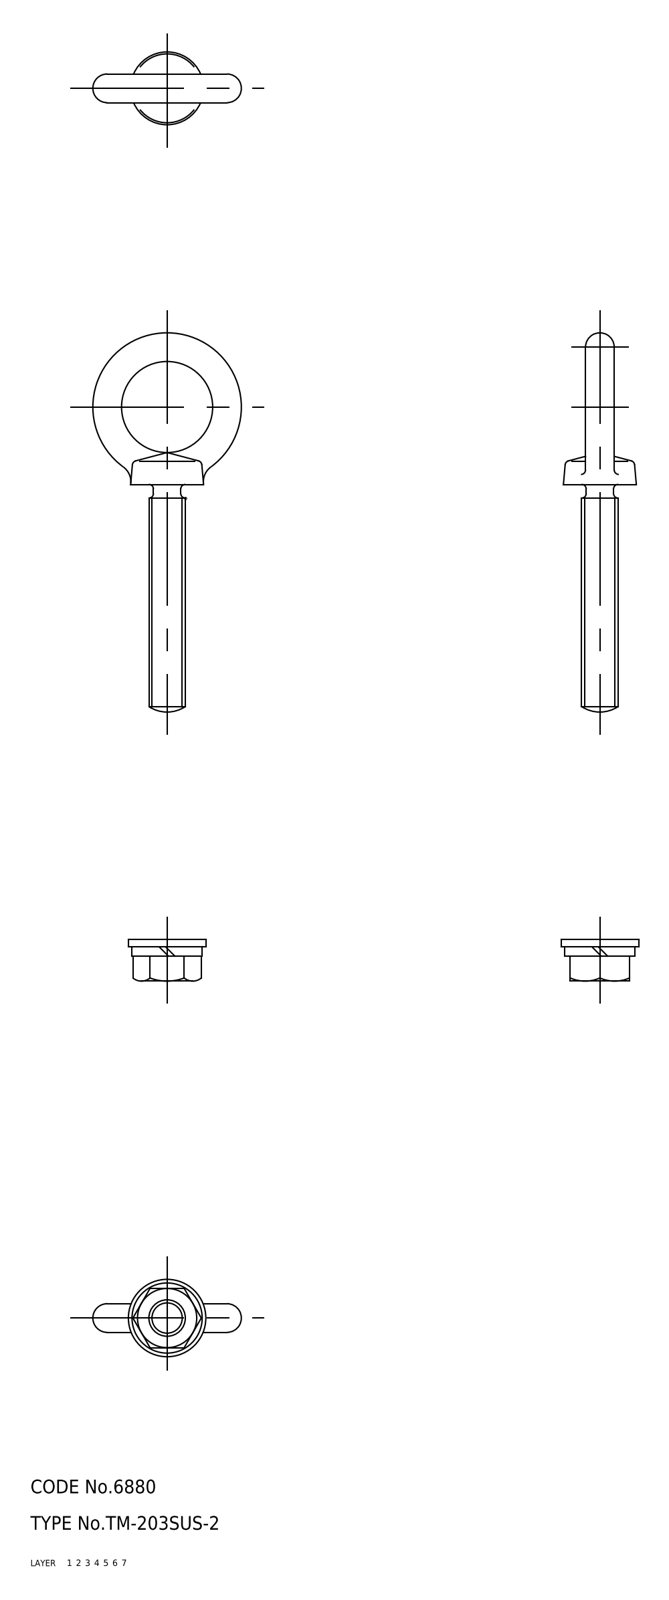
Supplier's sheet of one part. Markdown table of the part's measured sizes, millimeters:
| quantity | value |
| --- | --- |
| part name | TM_203SUS_2 |
| STEP written by | SolidWorks 2003240 (AUTOMOTIVE_DESIGN) |
| units | millimeters |
| bodies | 4 solids, 52 faces (13 planar, 12 cylindrical, 27 other) |
| overall size | 83.3 × 32.6 × 17 |
| volume | 6 878 mm³ |
| surface area | 4 658 mm² |
| round holes (diameter × count) | 8 × 1 |
| round bosses / shafts (diameter × count) | 17 × 1, 15.4 × 1 |
| main face-to-face distances | 1.6, 2, 3.6, 13, 5.5, 7.5, 9.1 |
